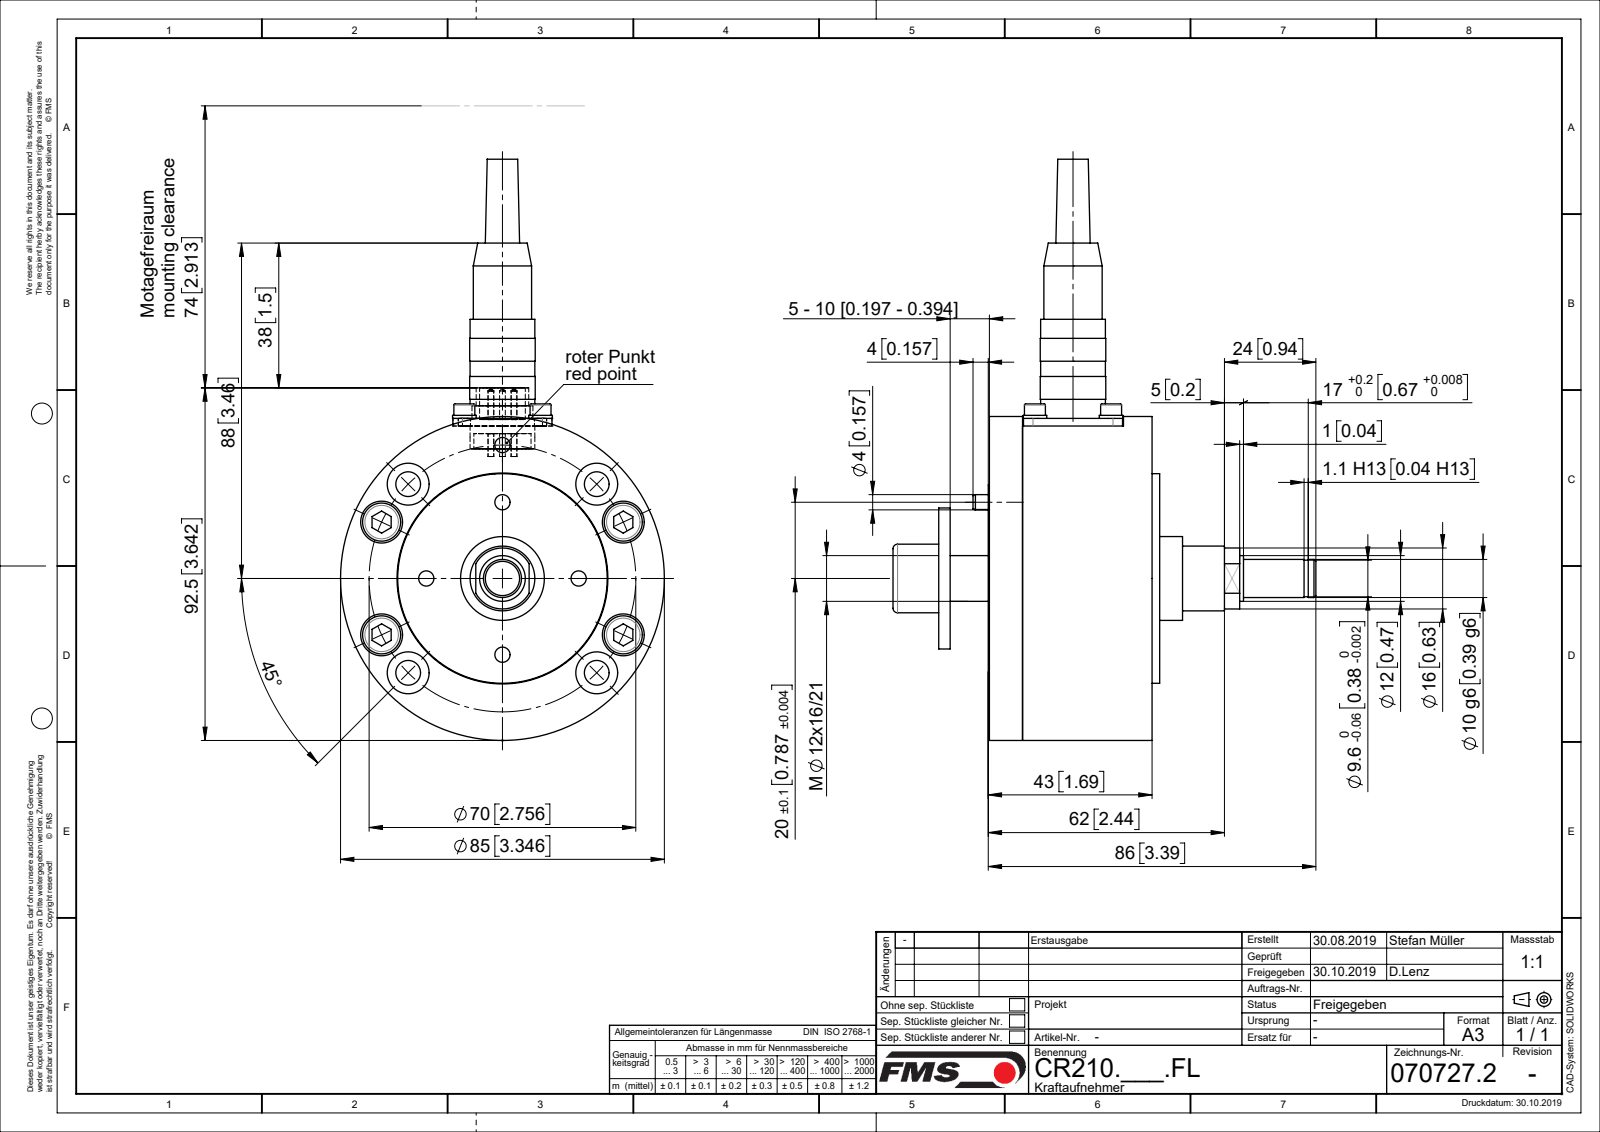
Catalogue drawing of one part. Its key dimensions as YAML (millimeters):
part_name: "ZEICHNUNG4; C0707272; C0709081; C0612056 (+8 more)"
step_written_by: "Mechanical Desktop 2009 (CONFIG_CONTROL_DESIGN)"
units: millimeters
bodies: {solids: 26, faces: 484, planar: 149, cylindrical: 249, other: 86}
overall_size: [152.5, 112, 85]
volume: 220148
surface_area: 84519
round_holes:
  - {diameter: 6.5, count: 8}
  - {diameter: 11, count: 8}
  - {diameter: 2.6, count: 4}
  - {diameter: 3.2, count: 4}
  - {diameter: 4, count: 4}
  - {diameter: 5.15, count: 4}
  - {diameter: 7, count: 4}
  - {diameter: 7.15, count: 1}
  - {diameter: 10.68, count: 1}
  - {diameter: 12, count: 1}
  - {diameter: 13, count: 1}
  - {diameter: 15, count: 1}
round_bosses_or_shafts:
  - {diameter: 10, count: 5}
  - {diameter: 1.5, count: 5}
  - {diameter: 6.2, count: 4}
  - {diameter: 6, count: 4}
  - {diameter: 5.5, count: 4}
  - {diameter: 5, count: 4}
  - {diameter: 3, count: 4}
  - {diameter: 17, count: 2}
partial_cylinders:
  - {radius: 2.5, count: 4}
  - {radius: 5, count: 2}
  - {radius: 8, count: 1}
face_to_face_distances: [6, 3, 9, 45, 10, 2, 34, 40, 43, 42]
hole_center_spacings: [20, 25.2, 35, 51.14, 28.28, 12.16, 14.14, 18.87]
